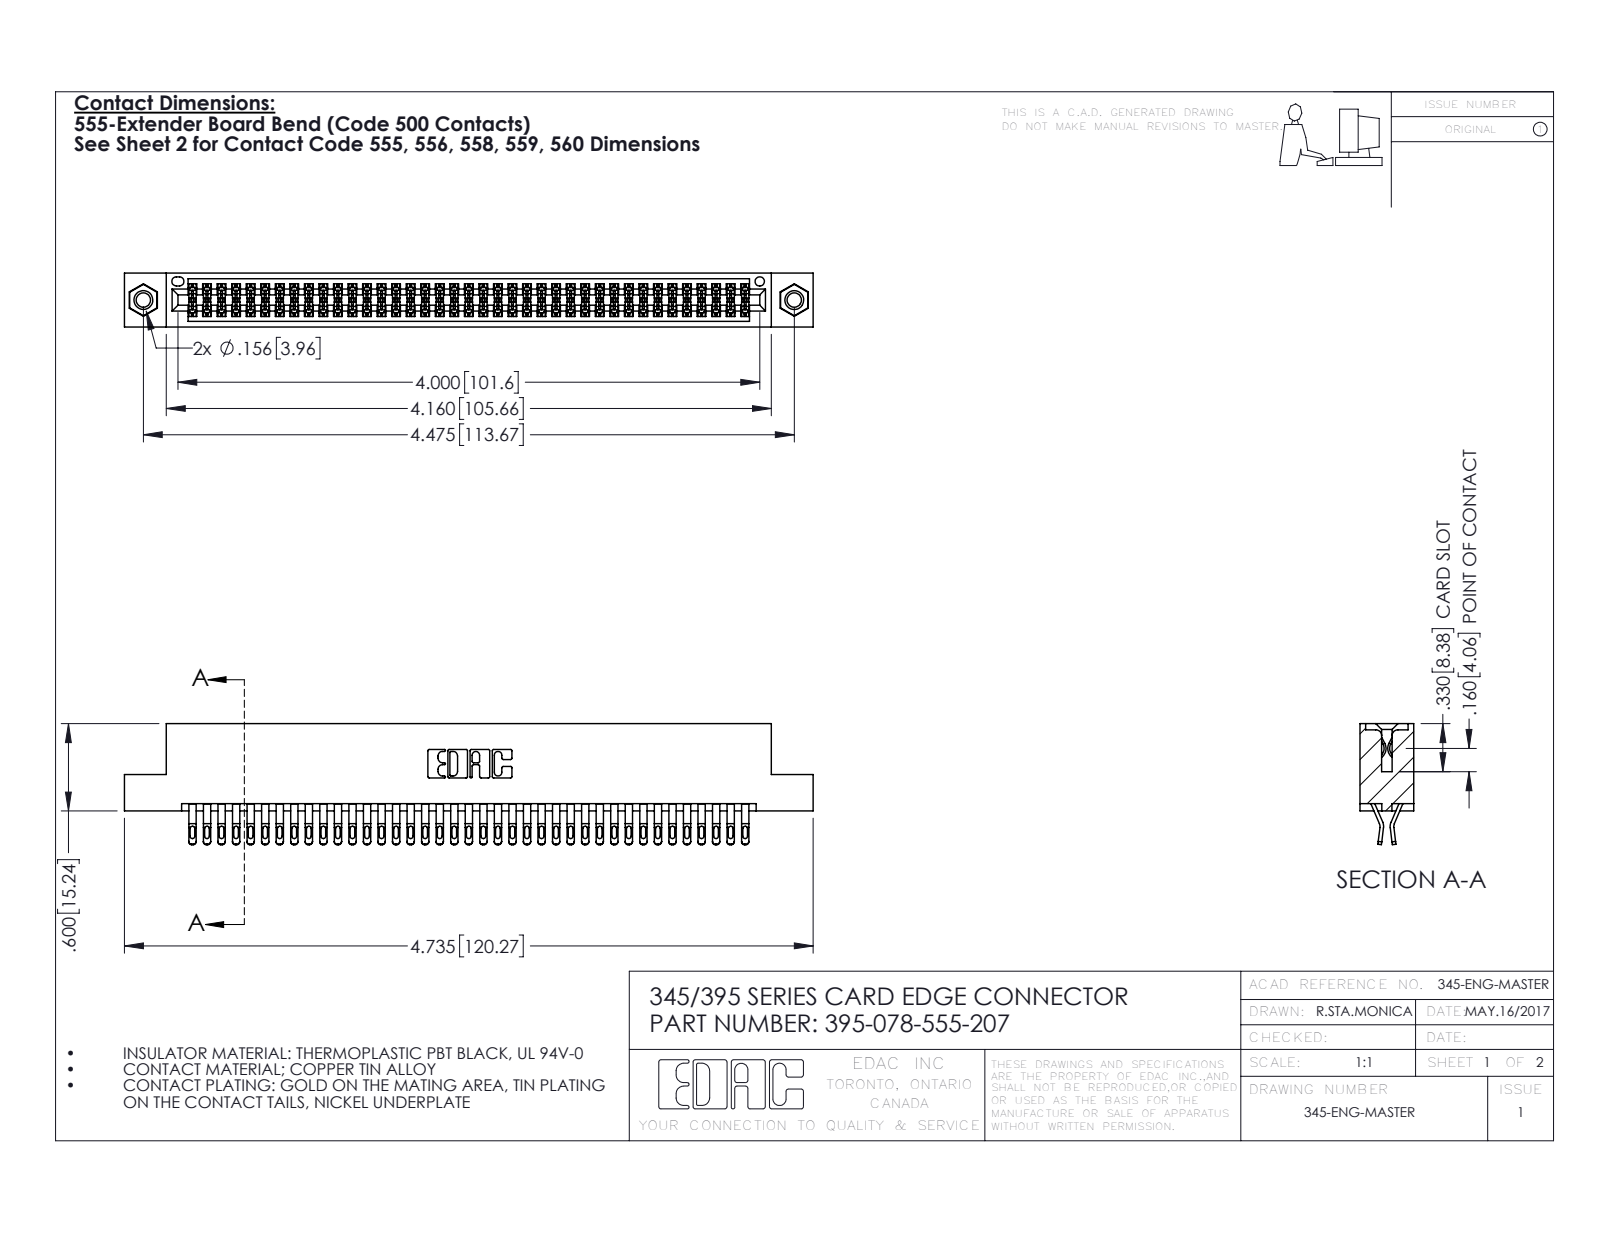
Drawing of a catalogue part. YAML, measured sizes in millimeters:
part_name: "395-078-555-207; 345 Part_Flush Mounting Lugs - 0.156 Dia-TI; 345-250-001_345-250-005-103; 345-292-001_555 Tail"
step_written_by: "SolidWorks 2016 (CONFIG_CONTROL_DESIGN)"
units: millimeters
bodies: {solids: 81, faces: 4554, planar: 2530, cylindrical: 2008, other: 16}
overall_size: [120.3, 21.1, 9.4]
volume: 11900
surface_area: 18300
round_holes:
  - {diameter: 2.5, count: 2}
  - {diameter: 3.2, count: 2}
  - {diameter: 4, count: 2}
  - {diameter: 1.6, count: 1}
round_bosses_or_shafts:
  - {diameter: 3.9, count: 2}
partial_cylinders:
  - {radius: 0.4, count: 195}
  - {radius: 0.5, count: 156}
  - {radius: 0.2, count: 117}
  - {radius: 0.3, count: 22}
  - {radius: 0.2, count: 6}
  - {radius: 0.8, count: 6}
  - {radius: 0.7, count: 3}
  - {radius: 0.3, count: 2}
face_to_face_distances: [1.8, 7.6, 0.6, 9.4, 5.1, 2.5, 6.9, 5.7, 4.4, 3.8]
hole_center_spacings: [6.9, 107.7, 113.7]
